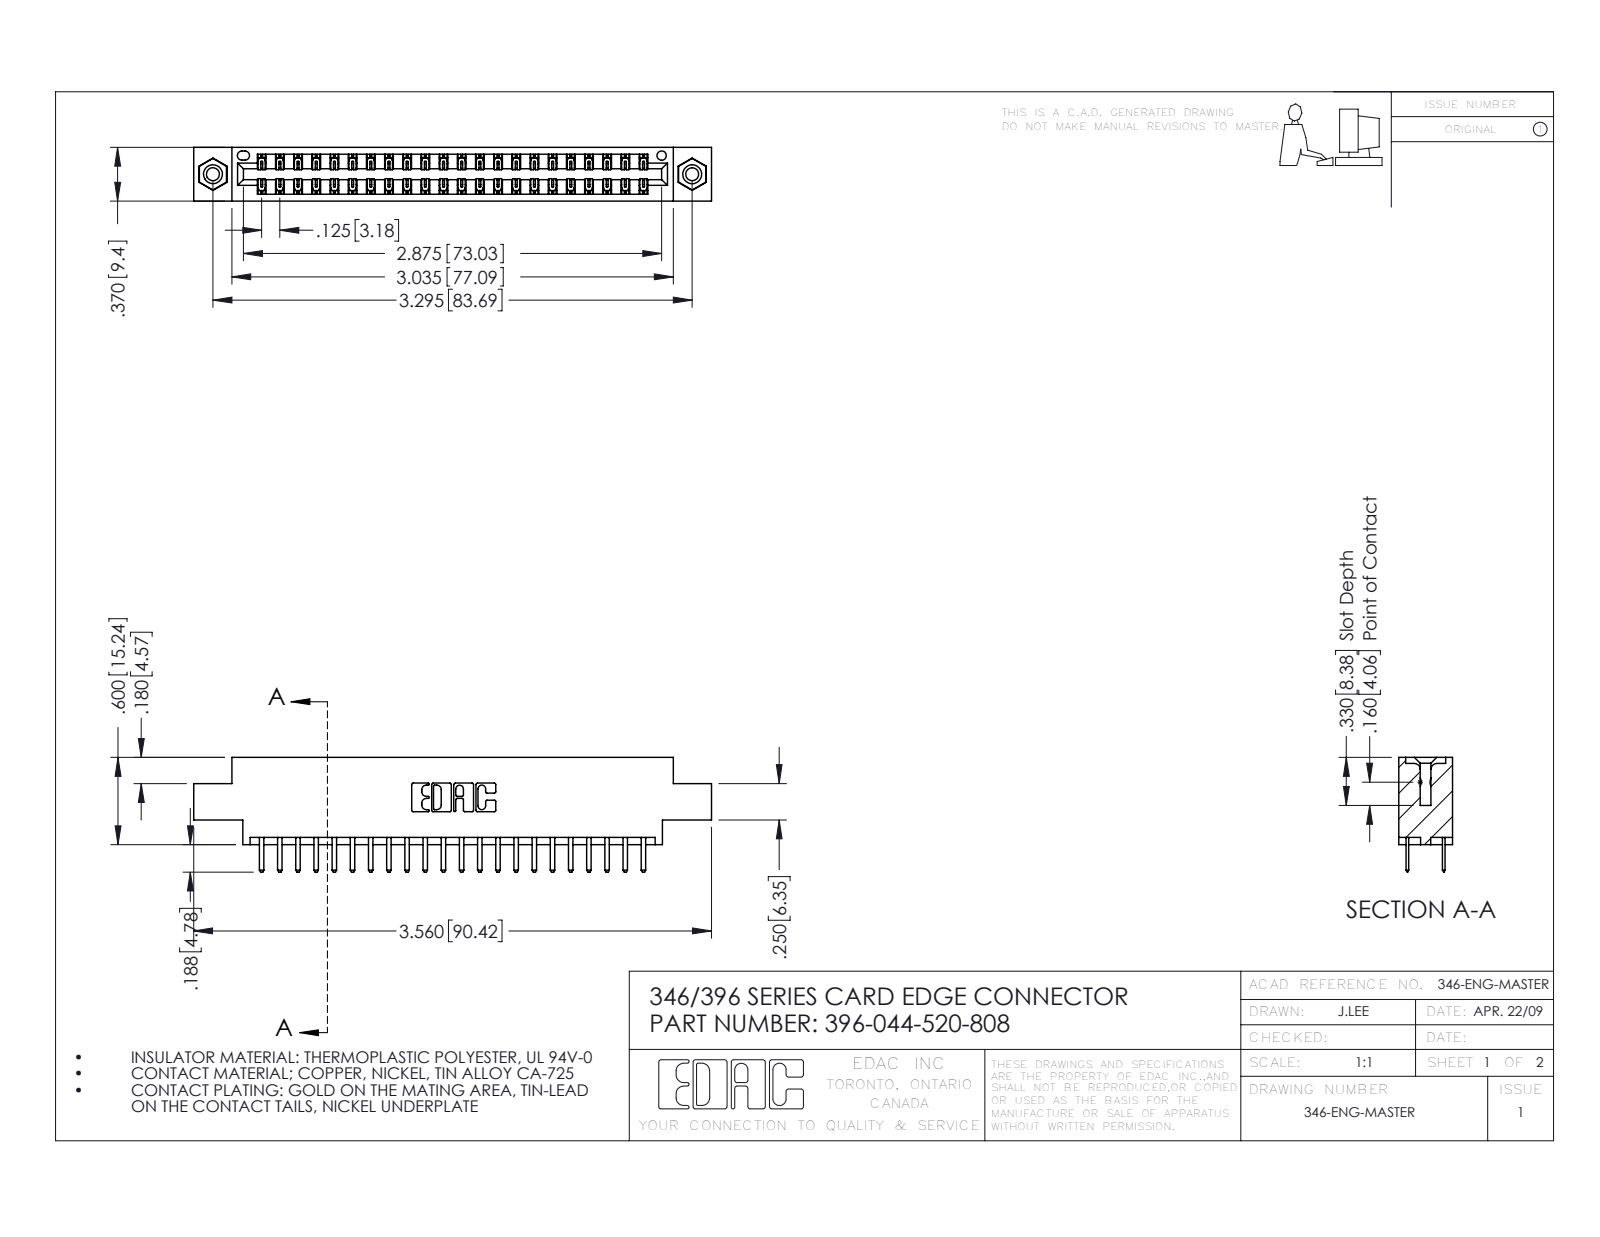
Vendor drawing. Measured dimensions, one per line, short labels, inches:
name: 396-044-520-808; 345-292-001_345-293-120; 345-250-001_345-250-003-102; 346 Part_0.170 Offset - 0.156 Dia-TI
written by: SolidWorks 2016 (CONFIG_CONTROL_DESIGN)
unit: in
bodies: 47 solids, 2650 faces (1740 planar, 894 cylindrical, 16 other)
size: 3.56 × 0.788 × 0.37
volume: 0.518 in³; area: 17.82 in²
holes: 2× ⌀0.089, 2× ⌀0.125, 2× ⌀0.156, 1× ⌀0.064
bosses: 2× ⌀0.155
rounds: 66× R0.006, 48× R0.01, 22× R0.01, 6× R0.007, 6× R0.031, 3× R0.026, 2× R0.014, 2× R0.022
face distances: 0.048, 0.322, 0.25, 0.37, 0.275, 0.072, 0.298, 0.025, 0.222, 0.148
hole spacings: 0.246, 3.087, 3.295
